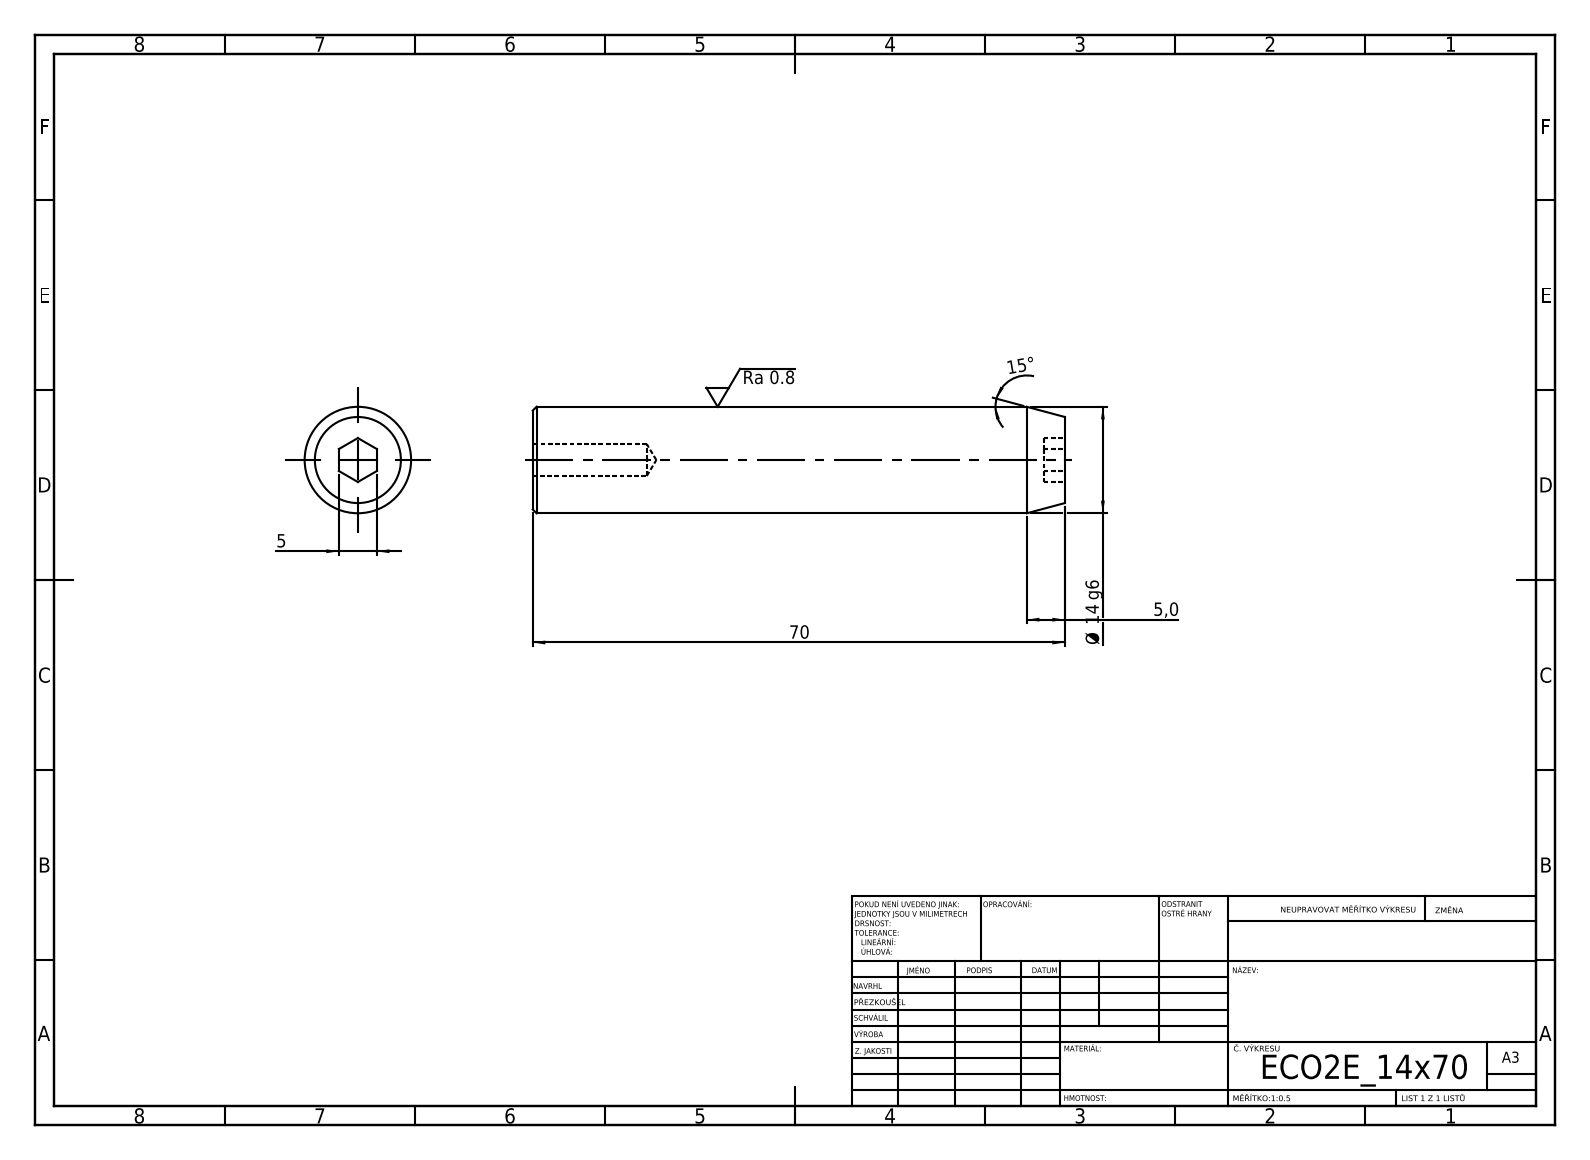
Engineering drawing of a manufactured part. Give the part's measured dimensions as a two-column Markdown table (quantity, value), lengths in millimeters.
| quantity | value |
| --- | --- |
| STEP written by | SolidWorks 2019 (CONFIG_CONTROL_DESIGN) |
| units | millimeters |
| bodies | 1 solid, 19 faces (9 planar, 4 cylindrical, 6 other) |
| overall size | 70 × 14 × 14 |
| volume | 10 358 mm³ |
| surface area | 3 555 mm² |
| round holes (diameter × count) | 4.2 × 1 |
| round bosses / shafts (diameter × count) | 14 × 1 |
| main face-to-face distances | 70, 5, 2.8, 67.2 |
